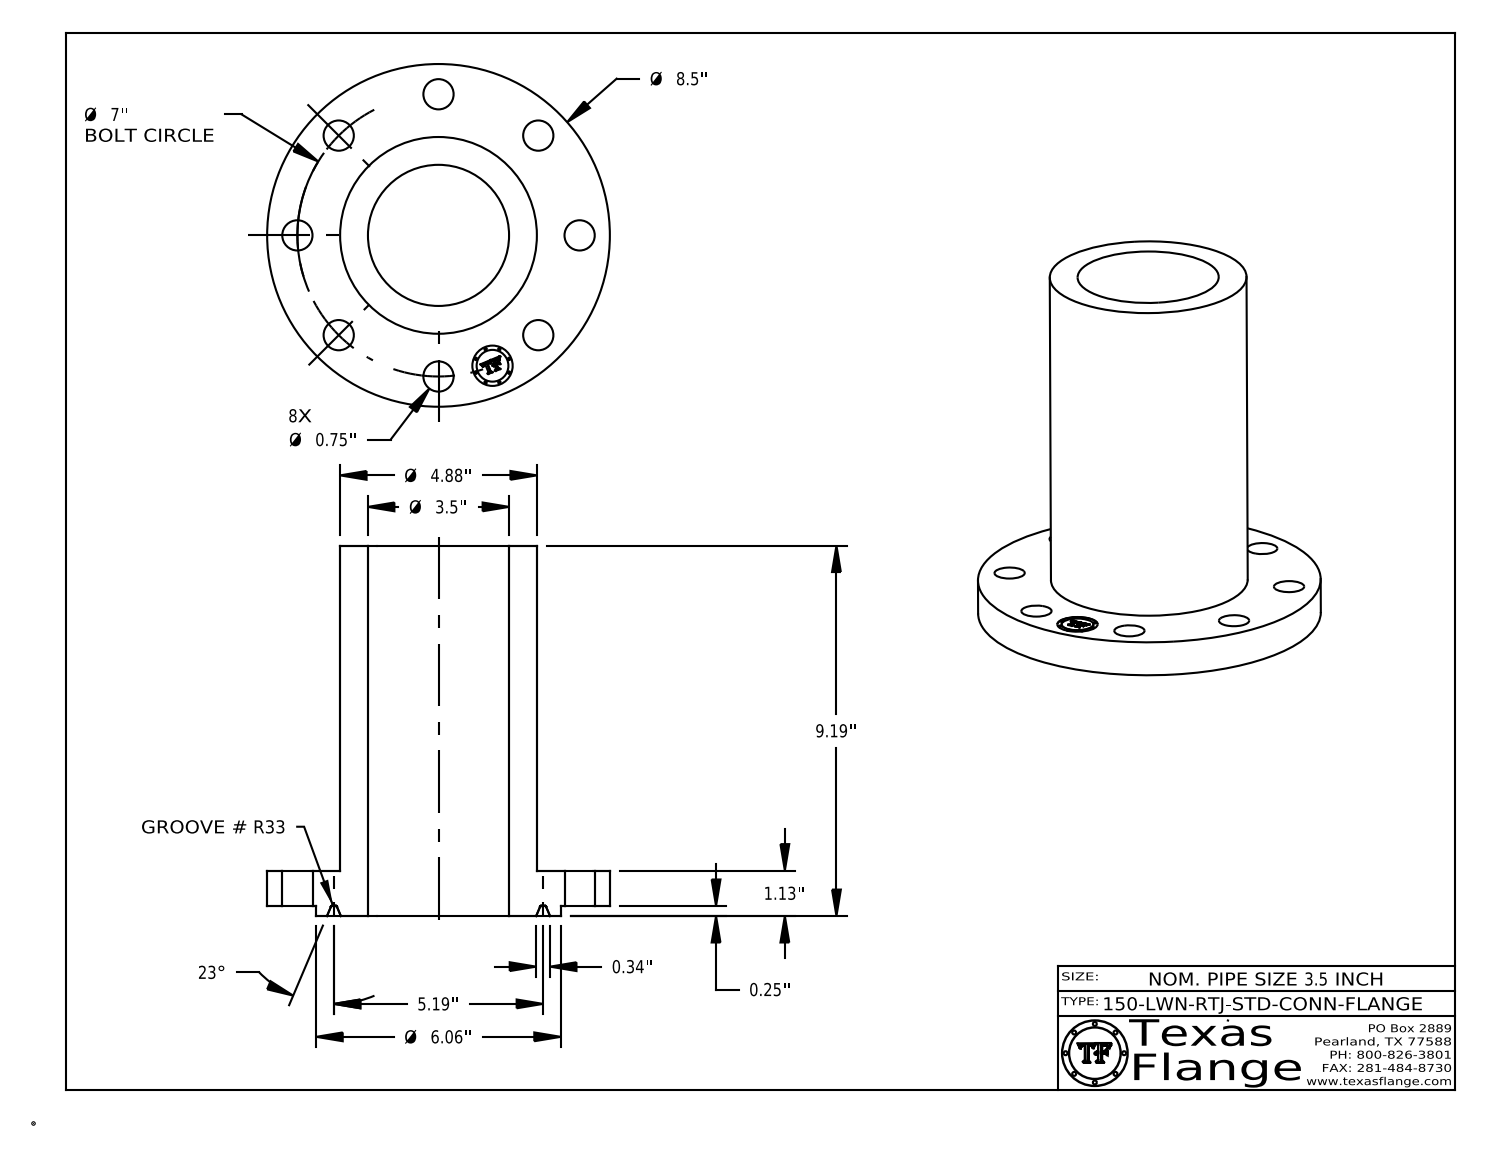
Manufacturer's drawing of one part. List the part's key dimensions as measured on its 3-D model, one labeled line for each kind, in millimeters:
Part name (STEP PRODUCT): 3.5-150-LWN-RTJ-STD-CONN-FLANGE
STEP written by: CATIA V5 STEP AP214 (AUTOMOTIVE_DESIGN)
Units: millimetres
Bodies: 1 solid, 423 faces (371 planar, 44 cylindrical, 8 other)
Overall size (bounding box): 233.4 × 215.9 × 215.9
Volume: 1 889 000 mm³ · Surface area: 233 400 mm²
Round holes (diameter × count): ⌀19.1 ×8, ⌀25.4 ×1, ⌀88.9 ×1
Round bosses / shafts (diameter × count): ⌀1.5 ×8, ⌀215.9 ×1, ⌀154 ×1, ⌀124 ×1, ⌀20 ×1
Main face-to-face distances: 22.3, 6.4, 28.7, 233.3, 227, 204.7, 28.5, 22.1, 204.9, 7.6
Hole centre spacings: 88.9, 68, 125.7, 164.3, 34.7, 98.8, 147.8, 174.4
